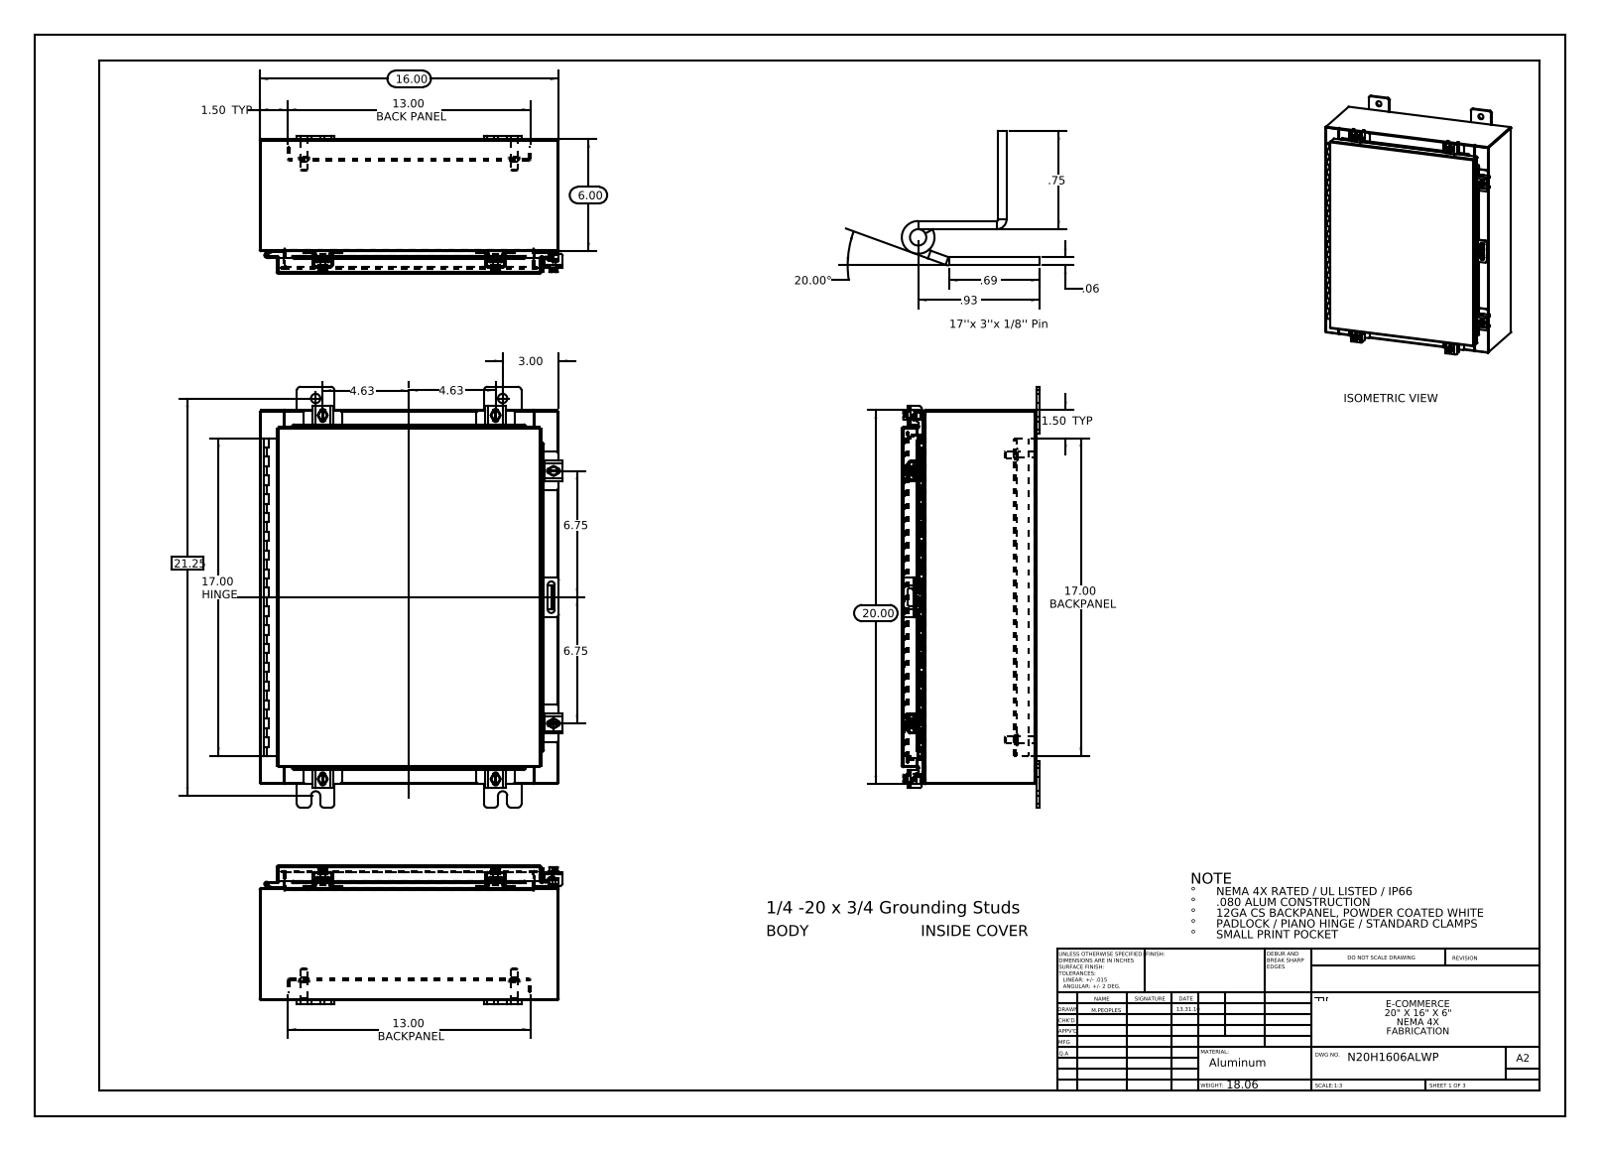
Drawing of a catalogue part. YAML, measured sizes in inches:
part_name: "N20H1606ALWP Clamp Top; N20H1606ALWP 125 Pin Hinge; N20H1606ALWP Standard Clamps; N20H1606ALWP Clamp Assembly (+8 more)"
step_written_by: "SolidWorks 2013 (CONFIG_CONTROL_DESIGN)"
units: inches
bodies: {solids: 47, faces: 1613, planar: 860, cylindrical: 657, other: 96}
overall_size: [22.5, 16.211, 7.389]
volume: 124.9
surface_area: 3149
round_holes:
  - {diameter: 0.5, count: 8}
  - {diameter: 0.213, count: 6}
  - {diameter: 0.26, count: 6}
  - {diameter: 0.125, count: 2}
  - {diameter: 0.125, count: 1}
round_bosses_or_shafts:
  - {diameter: 0.25, count: 7}
  - {diameter: 0.5, count: 6}
  - {diameter: 0.399, count: 6}
  - {diameter: 0.625, count: 4}
  - {diameter: 0.375, count: 4}
  - {diameter: 0.33, count: 4}
partial_cylinders:
  - {radius: 0.06, count: 30}
  - {radius: 0.013, count: 25}
  - {radius: 0.19, count: 24}
  - {radius: 0.088, count: 21}
  - {radius: 0.12, count: 12}
  - {radius: 0.141, count: 12}
  - {radius: 0.125, count: 10}
  - {radius: 0.05, count: 9}
face_to_face_distances: [0.075, 7.126, 7.201, 7.051, 0.104, 15.925, 1, 1.075, 6.051, 6.126]
hole_center_spacings: [17.38, 1.858, 2.276, 2.326, 2.326, 3.065, 4.297, 9.25]
